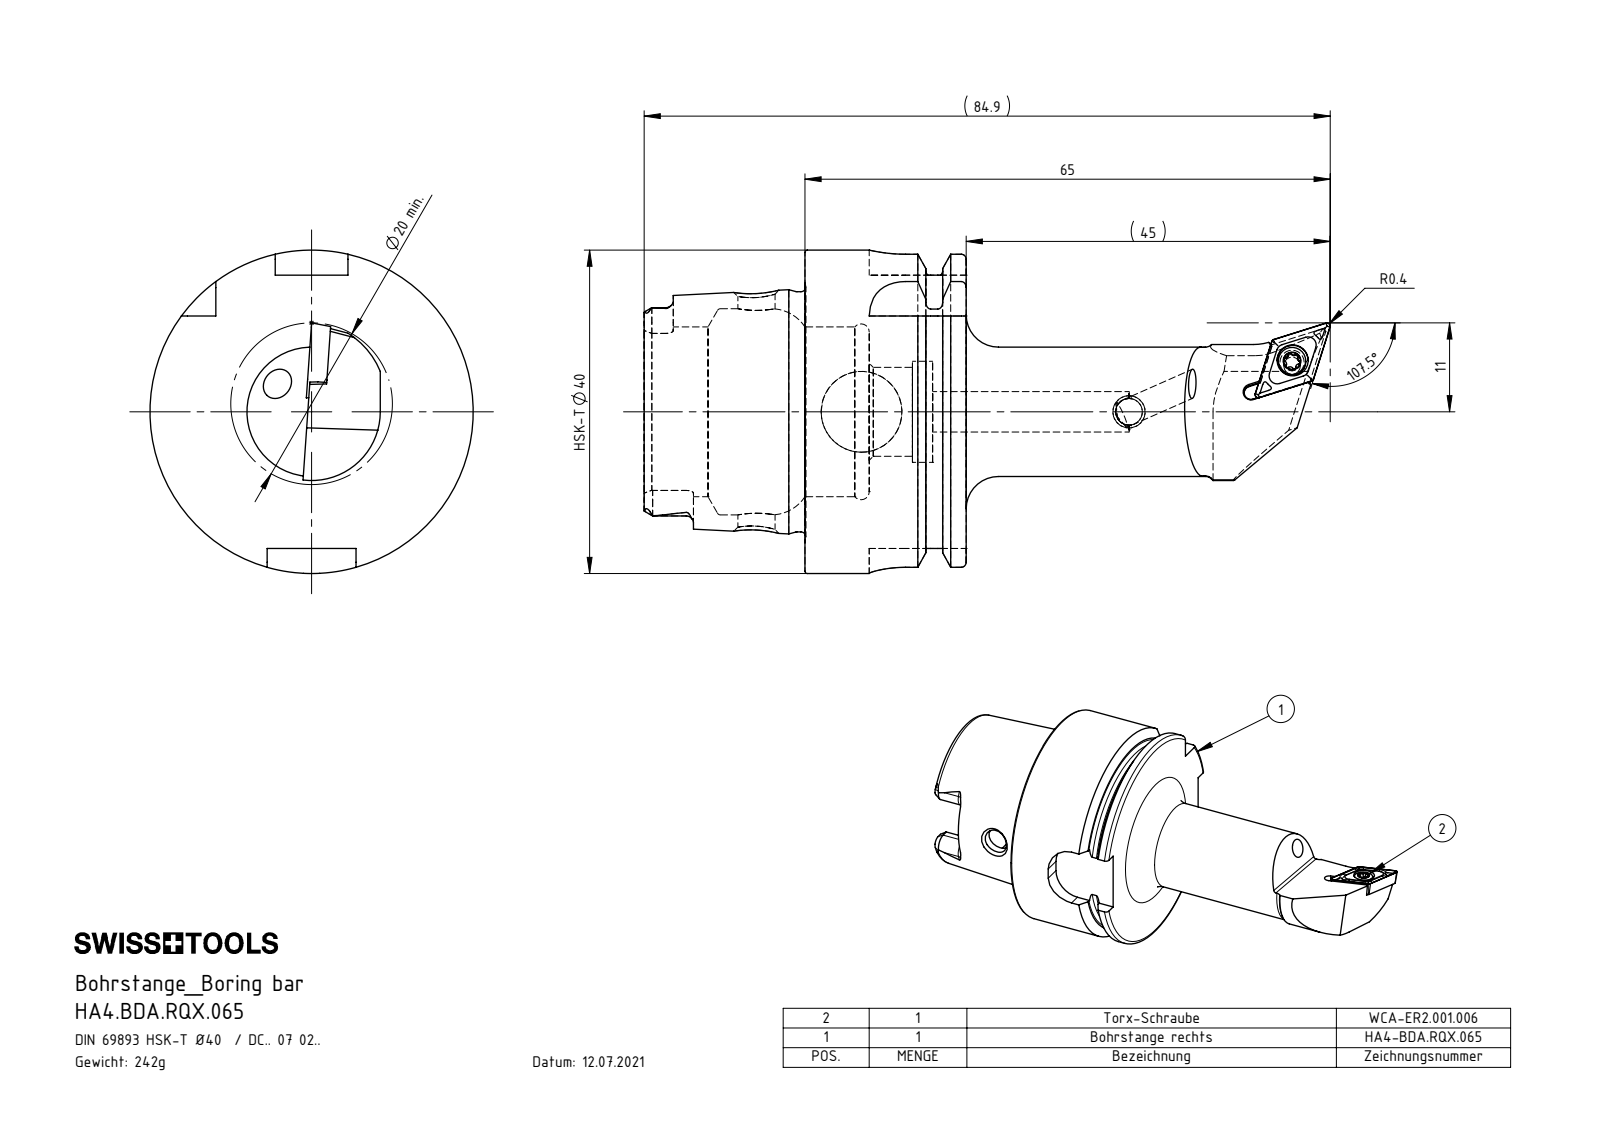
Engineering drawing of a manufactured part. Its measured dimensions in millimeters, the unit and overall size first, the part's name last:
Units: millimetres
Overall size (bounding box): 84.9 × 40 × 40
Round holes (diameter × count): ⌀3.3 ×2, ⌀2.05 ×1, ⌀2.8 ×1, ⌀3 ×1, ⌀3.85 ×1, ⌀4.6 ×1, ⌀5 ×1, ⌀10 ×1, ⌀11 ×1, ⌀12.5 ×1, ⌀21 ×1, ⌀25.5 ×1
Round bosses / shafts (diameter × count): ⌀40 ×1, ⌀34.75 ×1, ⌀29.71 ×1, ⌀16 ×1, ⌀4 ×1, ⌀3.4 ×1, ⌀2.5 ×1
Partial cylindrical surfaces — rounded edges, fillets, slot ends (radius × count): R0.21 ×6, R0.9 ×6, R1.88 ×4, R4.5 ×4, R0.36 ×3, R0.36 ×3, R0.5 ×1, R0.85 ×1
Main face-to-face distances: 19.95, 7.95, 12, 19.9, 27.85, 39.85, 35.7, 15.8, 7.85, 4.15
Hole centre spacings: 33.1
Volume: 30 901 mm³ · Surface area: 12 399 mm²
Bodies: 5 solids, 238 faces (82 planar, 61 cylindrical, 95 other)
Part name (STEP PRODUCT): DCMT070204; HA4.BDA.RQX.065; WCA-ER2.001.006_A; HA4-BDA.RQX.065_A_Fertigbearbeitung (+1 more)
STEP written by: SolidWorks 2017 (AUTOMOTIVE_DESIGN)
